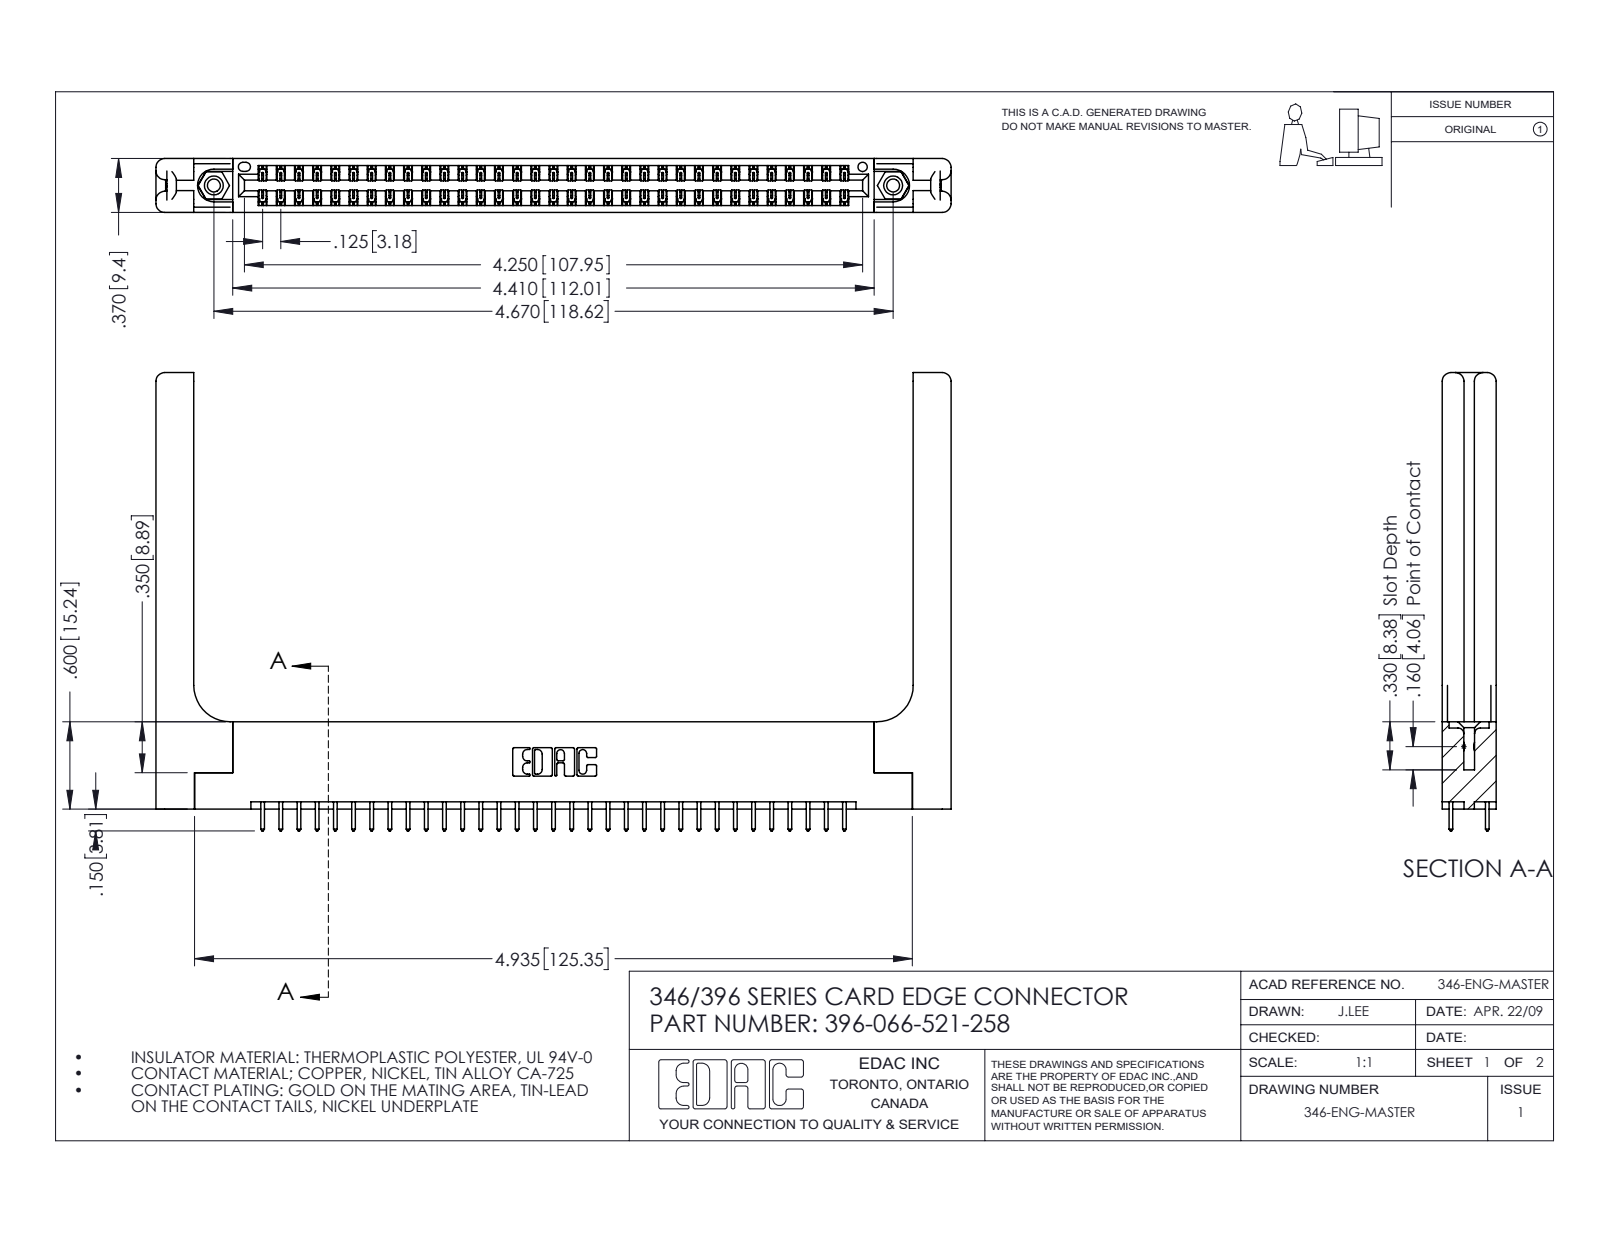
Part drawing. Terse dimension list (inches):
name: 345-250-001_345-250-001-102; 346-220-058_345-220-058; 396-066-521-258; 345-292-001_345-293-121 (+1 more)
written by: SolidWorks 2016 (CONFIG_CONTROL_DESIGN)
unit: in
bodies: 71 solids, 3810 faces (2534 planar, 1216 cylindrical, 60 other)
size: 5.466 × 3.15 × 0.37
volume: 1.278 in³; area: 35.85 in²
holes: 2× ⌀0.089, 2× ⌀0.125, 2× ⌀0.156, 1× ⌀0.064
bosses: 2× ⌀0.155
rounds: 99× R0.006, 66× R0.01, 22× R0.01, 16× R0.06, 6× R0.007, 6× R0.031, 3× R0.026, 2× R0.014
face distances: 0.37, 0.048, 0.322, 0.072, 0.148, 0.15, 0.25, 0.025, 0.298, 0.275
hole spacings: 0.246, 4.462, 4.67
